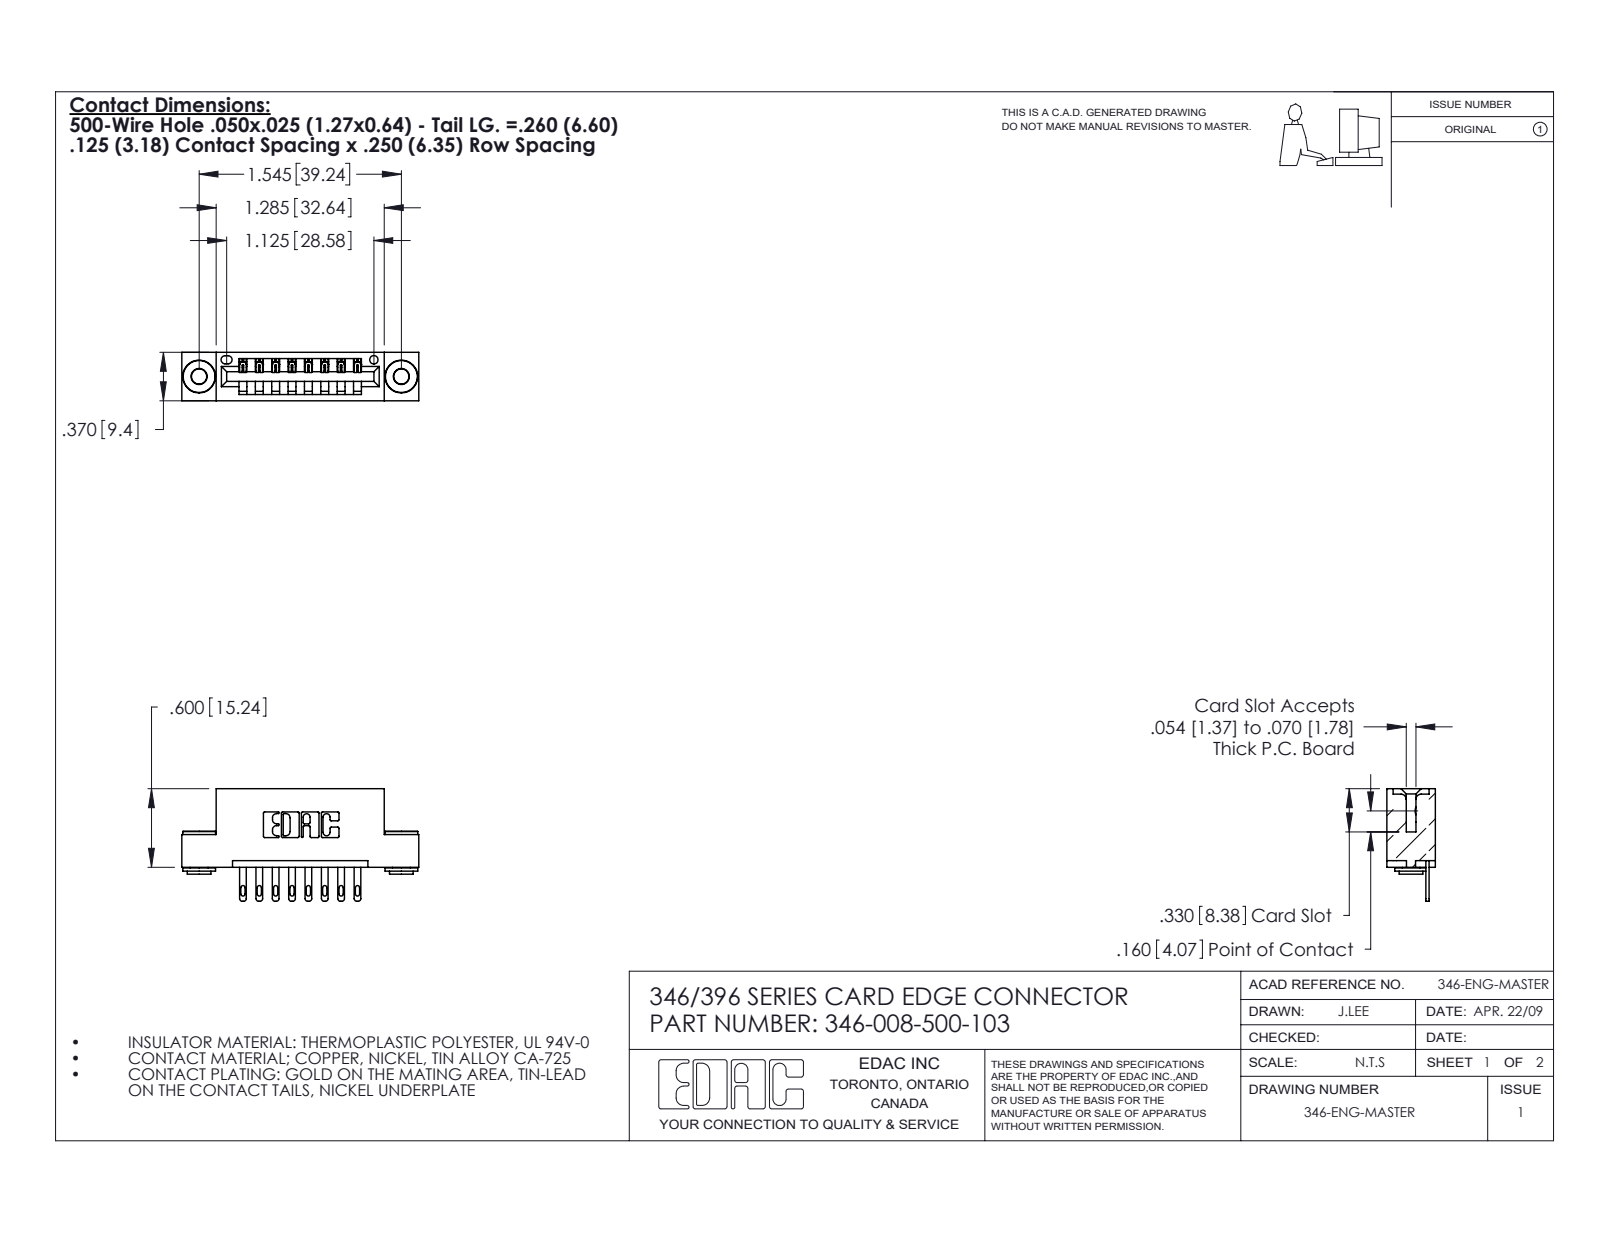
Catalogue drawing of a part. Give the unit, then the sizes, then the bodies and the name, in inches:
Units: inches
Overall size (bounding box): 1.81 × 0.86 × 0.37
Round holes (diameter × count): ⌀0.116 ×2, ⌀0.156 ×2, ⌀0.064 ×1
Round bosses / shafts (diameter × count): ⌀0.25 ×2, ⌀0.18 ×2, ⌀0.136 ×2
Partial cylindrical surfaces — rounded edges, fillets, slot ends (radius × count): R0.01 ×22, R0.006 ×16, R0.016 ×16, R0.02 ×16, R0.007 ×6, R0.031 ×6, R0.026 ×3, R0.031 ×2
Main face-to-face distances: 0.25, 0.37, 0.048, 0.322, 0.025, 0.5, 0.072, 0.298, 0.148, 0.222
Hole centre spacings: 0.246, 1.341, 1.545
Volume: 0.255 in³ · Surface area: 7.934 in²
Bodies: 11 solids, 606 faces (372 planar, 226 cylindrical, 8 other)
Part name (STEP PRODUCT): 346-008-500-103; 345-292-001_345-293-100; 345-250-002_345-250-002-102; 346 Part_Flush Mounting Lugs - 0.156 Dia-TH
STEP written by: SolidWorks 2020 (CONFIG_CONTROL_DESIGN)
